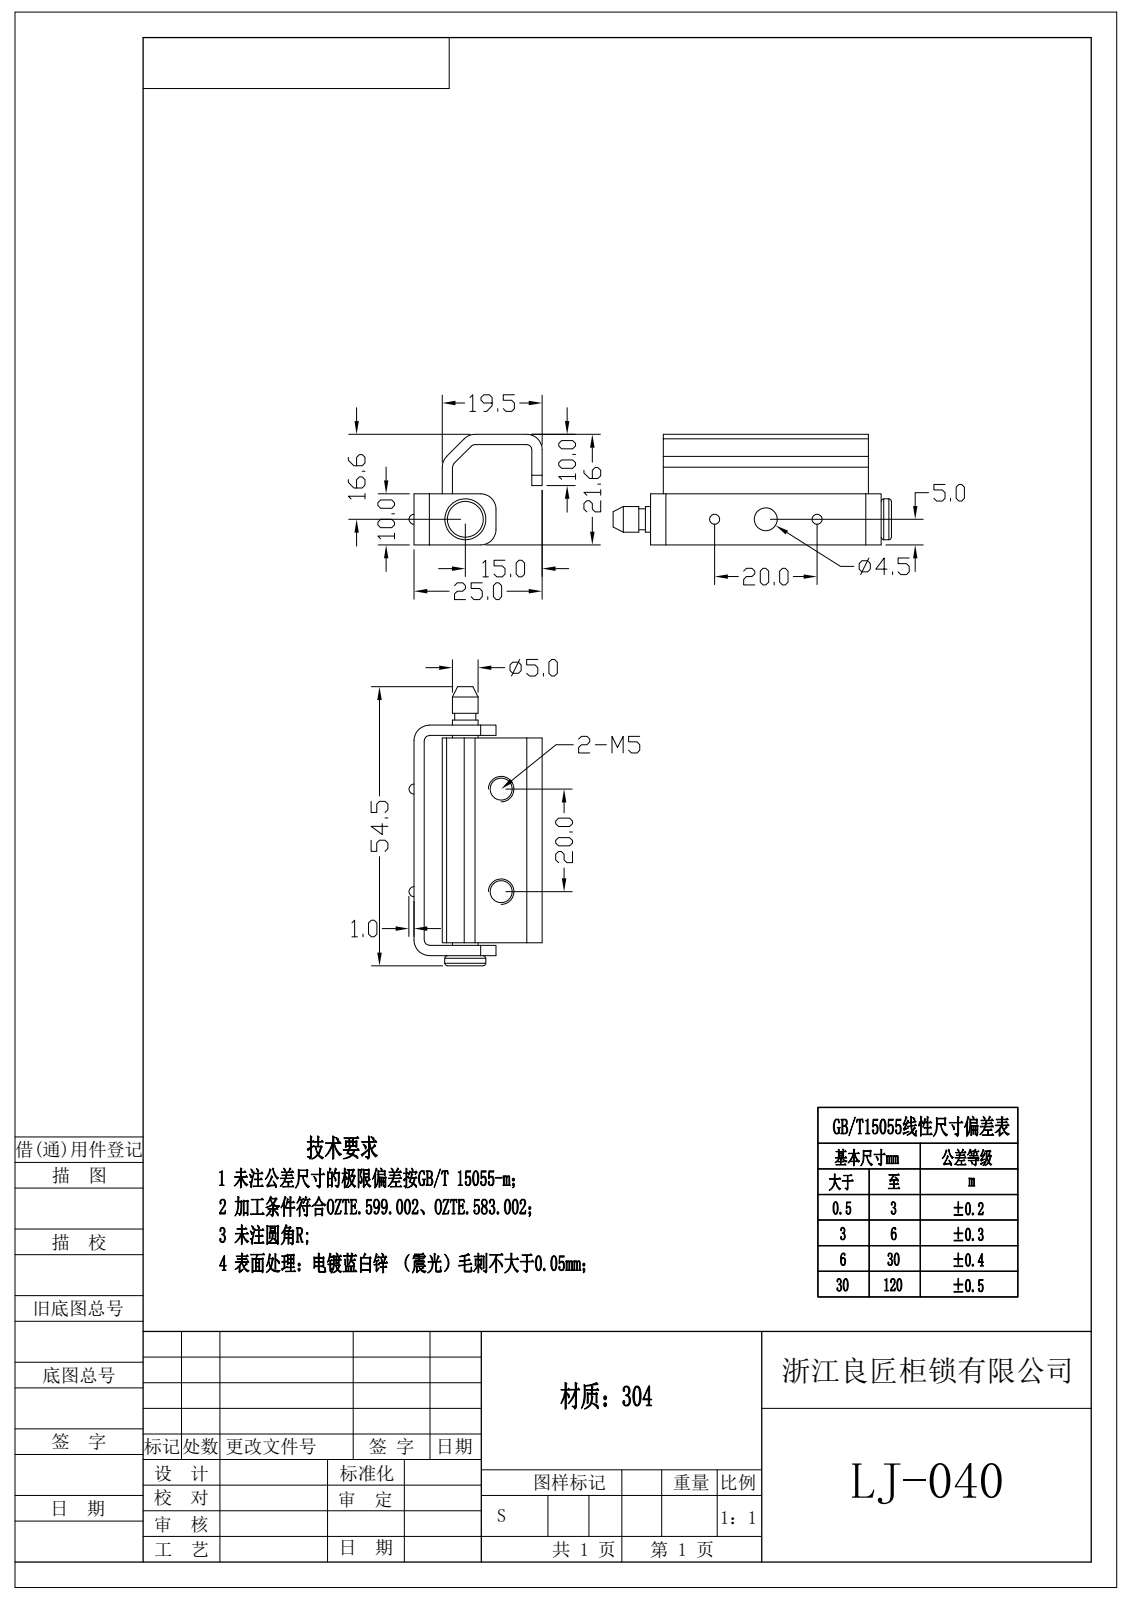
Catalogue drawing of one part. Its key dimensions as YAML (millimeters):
step_written_by: "Rhino 8.5 (CONFIG_CONTROL_DESIGN)"
units: millimeters
bodies: {solids: 3, faces: 73, planar: 27, cylindrical: 36, other: 10}
overall_size: [54.5, 27.1, 20]
volume: 6875
surface_area: 7578
round_holes:
  - {diameter: 4.6, count: 2}
  - {diameter: 4.5, count: 1}
  - {diameter: 5, count: 1}
  - {diameter: 5.2, count: 1}
round_bosses_or_shafts:
  - {diameter: 9, count: 1}
  - {diameter: 8, count: 1}
  - {diameter: 5, count: 1}
  - {diameter: 4.1, count: 1}
partial_cylinders:
  - {radius: 3, count: 7}
  - {radius: 1, count: 5}
  - {radius: 2, count: 2}
face_to_face_distances: [2, 24.1, 17.5, 22.1, 26.1, 2.5, 0.5, 10, 15.5, 19.5]
hole_center_spacings: [12.21, 0.5, 20]
